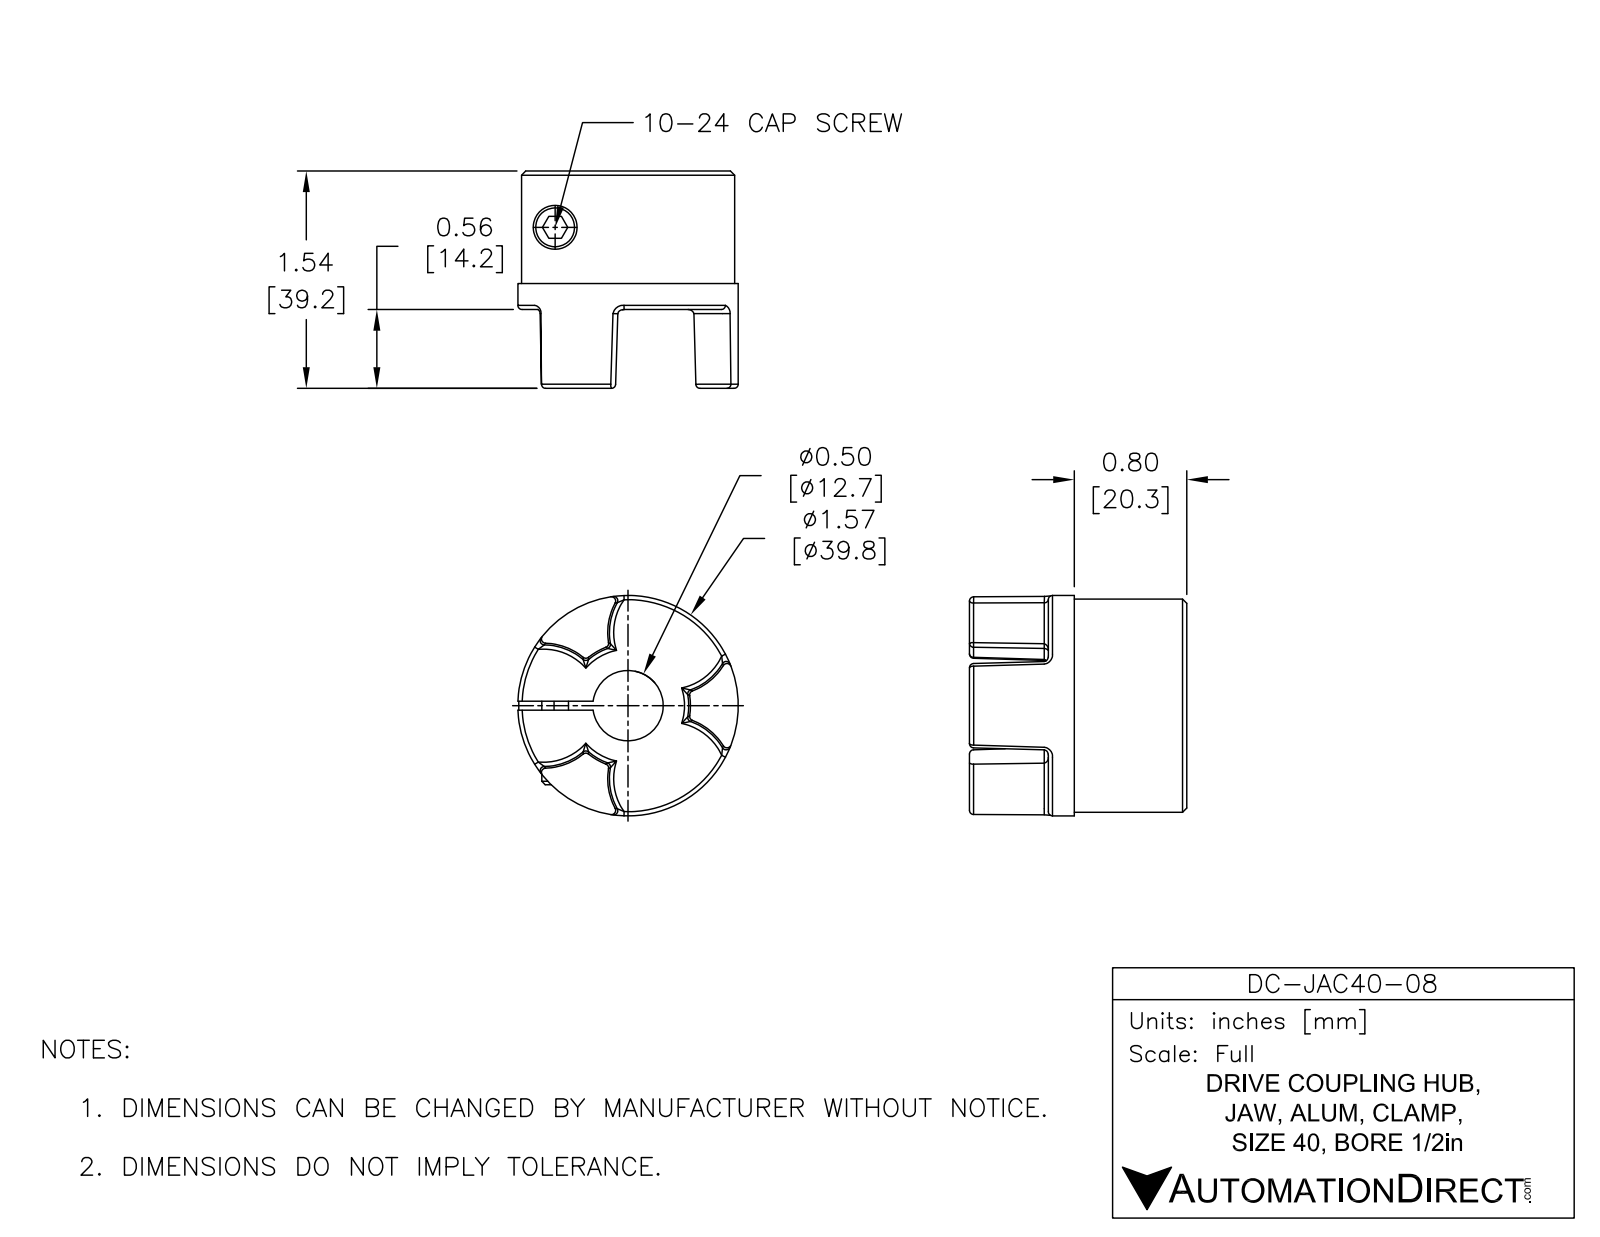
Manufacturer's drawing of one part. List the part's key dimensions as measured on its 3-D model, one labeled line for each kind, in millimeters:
Part name (STEP PRODUCT): DC-JAC40-08
STEP written by: SolidWorks 2015 (AUTOMOTIVE_DESIGN)
Units: millimetres
Bodies: 1 solid, 107 faces (12 planar, 17 cylindrical, 78 other)
Overall size (bounding box): 39.78 × 39.76 × 39.22
Volume: 28 620 mm³ · Surface area: 8 703 mm²
Round holes (diameter × count): ⌀5.11 ×1, ⌀8.36 ×1, ⌀12.7 ×1
Round bosses / shafts (diameter × count): ⌀39.78 ×1, ⌀38.48 ×1
Partial cylindrical surfaces — rounded edges, fillets, slot ends (radius × count): R0.76 ×2
Main face-to-face distances: 24.99, 1.6, 39.22, 14.23, 20.29, 4.7, 18.93, 3.99, 5.59
